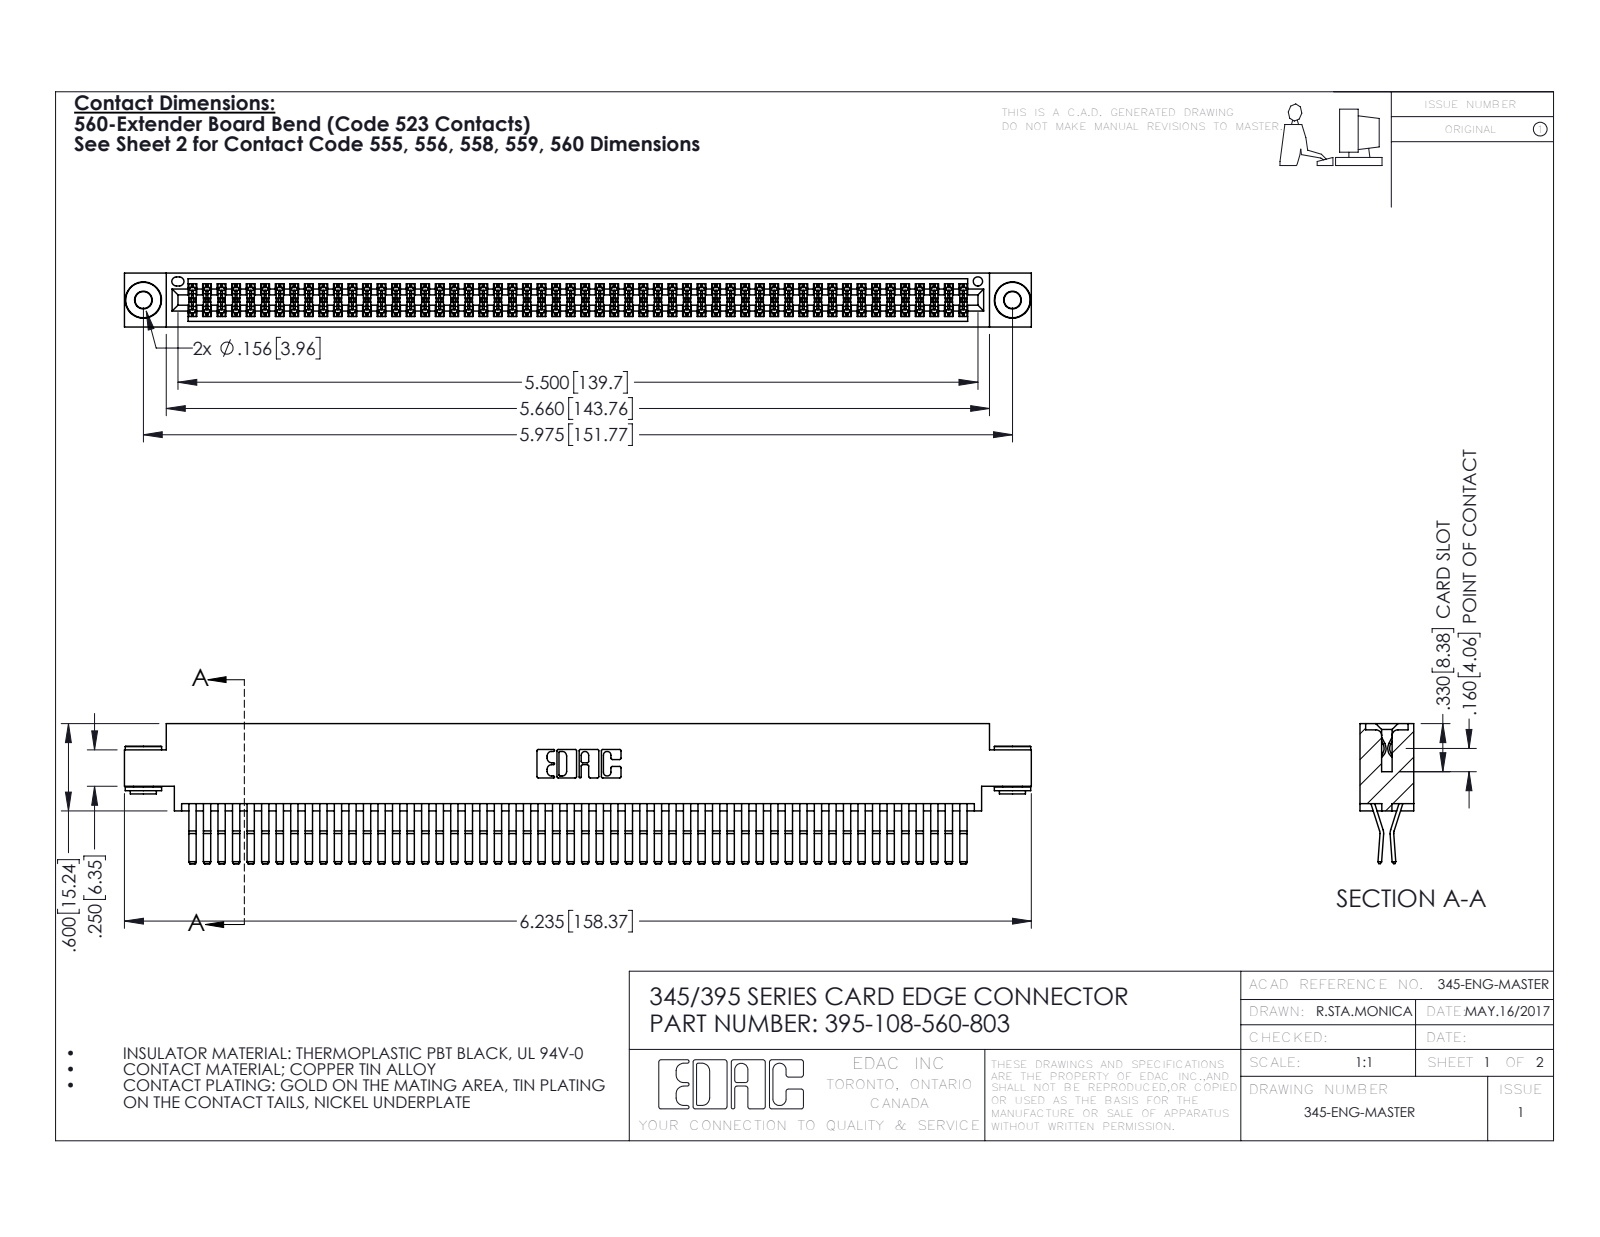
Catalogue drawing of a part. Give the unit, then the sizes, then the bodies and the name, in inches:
Units: inches
Overall size (bounding box): 6.235 × 0.962 × 0.37
Round holes (diameter × count): ⌀0.116 ×2, ⌀0.156 ×2, ⌀0.064 ×1
Round bosses / shafts (diameter × count): ⌀0.25 ×2, ⌀0.18 ×2, ⌀0.136 ×2
Partial cylindrical surfaces — rounded edges, fillets, slot ends (radius × count): R0.006 ×162, R0.01 ×22, R0.007 ×6, R0.031 ×6, R0.026 ×3, R0.01 ×2, R0.014 ×2, R0.019 ×2
Main face-to-face distances: 0.025, 0.072, 0.298, 0.37, 0.2, 0.098, 0.272, 0.225, 0.175, 0.149
Hole centre spacings: 0.27, 5.739, 5.975
Volume: 0.983 in³ · Surface area: 40.63 in²
Bodies: 111 solids, 5784 faces (3658 planar, 2118 cylindrical, 8 other)
Part name (STEP PRODUCT): 395-108-560-803; 345-292-001_560 Tail; 345 Part_0.170 Offset - 0.156 Dia-TH; 345-250-002_345-250-002-102
STEP written by: SolidWorks 2016 (CONFIG_CONTROL_DESIGN)
